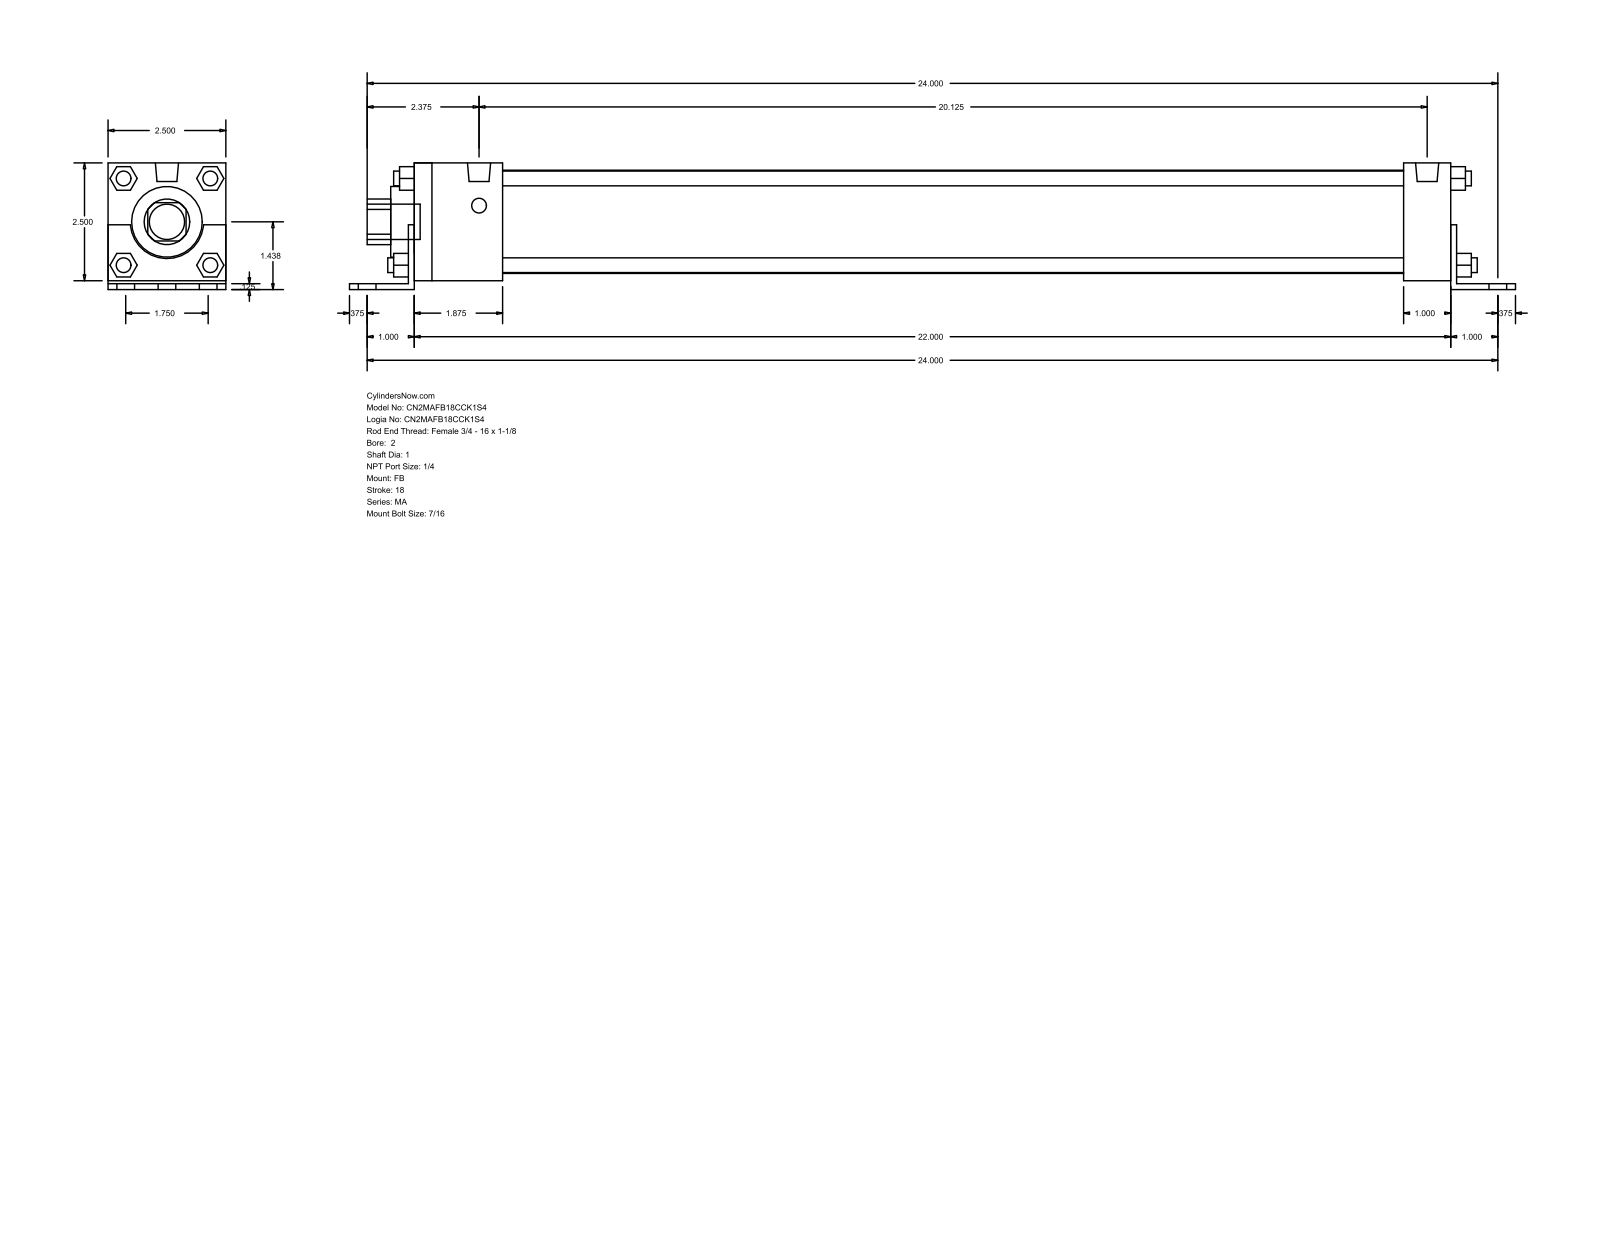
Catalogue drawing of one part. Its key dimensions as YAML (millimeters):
part_name: "MA_FB__0200_1"
step_written_by: "GSSL Pune (CONFIG_CONTROL_DESIGN)"
units: millimeters
bodies: {solids: 0, faces: 140, planar: 105, cylindrical: 35, other: 0}
overall_size: [628.65, 68.26, 63.5]
round_holes:
  - {diameter: 25.4, count: 1}
  - {diameter: 38.1, count: 1}
  - {diameter: 55.63, count: 1}
round_bosses_or_shafts:
  - {diameter: 7.94, count: 8}
  - {diameter: 11.11, count: 6}
  - {diameter: 12.49, count: 2}
  - {diameter: 19.05, count: 1}
partial_cylinders:
  - {radius: 12.29, count: 1}
  - {radius: 19.81, count: 1}
face_to_face_distances: [63.5, 3.17, 4.76, 68.26, 1.59, 65.09, 12.7, 3.18, 558.8, 561.98]
